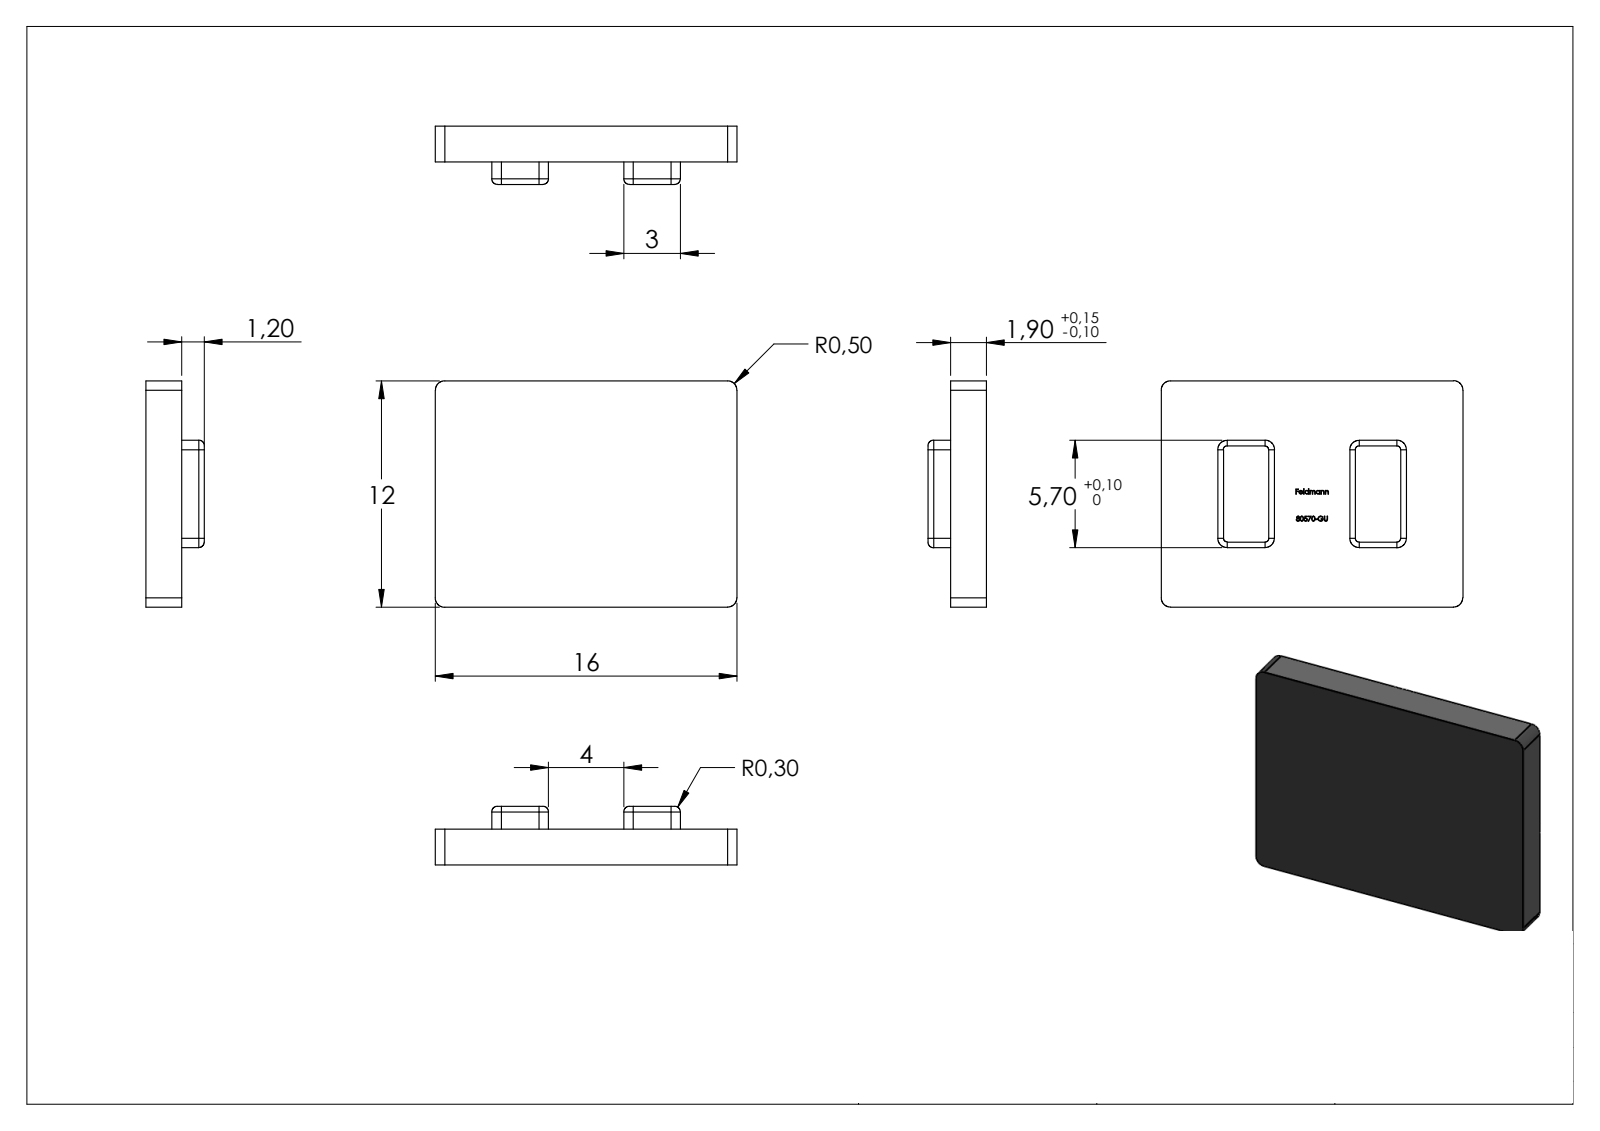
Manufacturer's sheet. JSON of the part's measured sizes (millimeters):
{"part_name": "80570-GU", "step_written_by": "SolidWorks 2015 (CONFIG_CONTROL_DESIGN)", "units": "millimeters", "bodies": {"solids": 1, "faces": 254, "planar": 119, "cylindrical": 20, "other": 115}, "overall_size": [16, 12, 3.1], "volume_mm3": 404, "surface_area_mm2": 526, "partial_cylinders_radius": [[0.5, 12], [0.3, 6]], "face_to_face_distances": [1.9, 12, 1.2, 3.1, 16, 3, 10, 6, 13, 7]}
